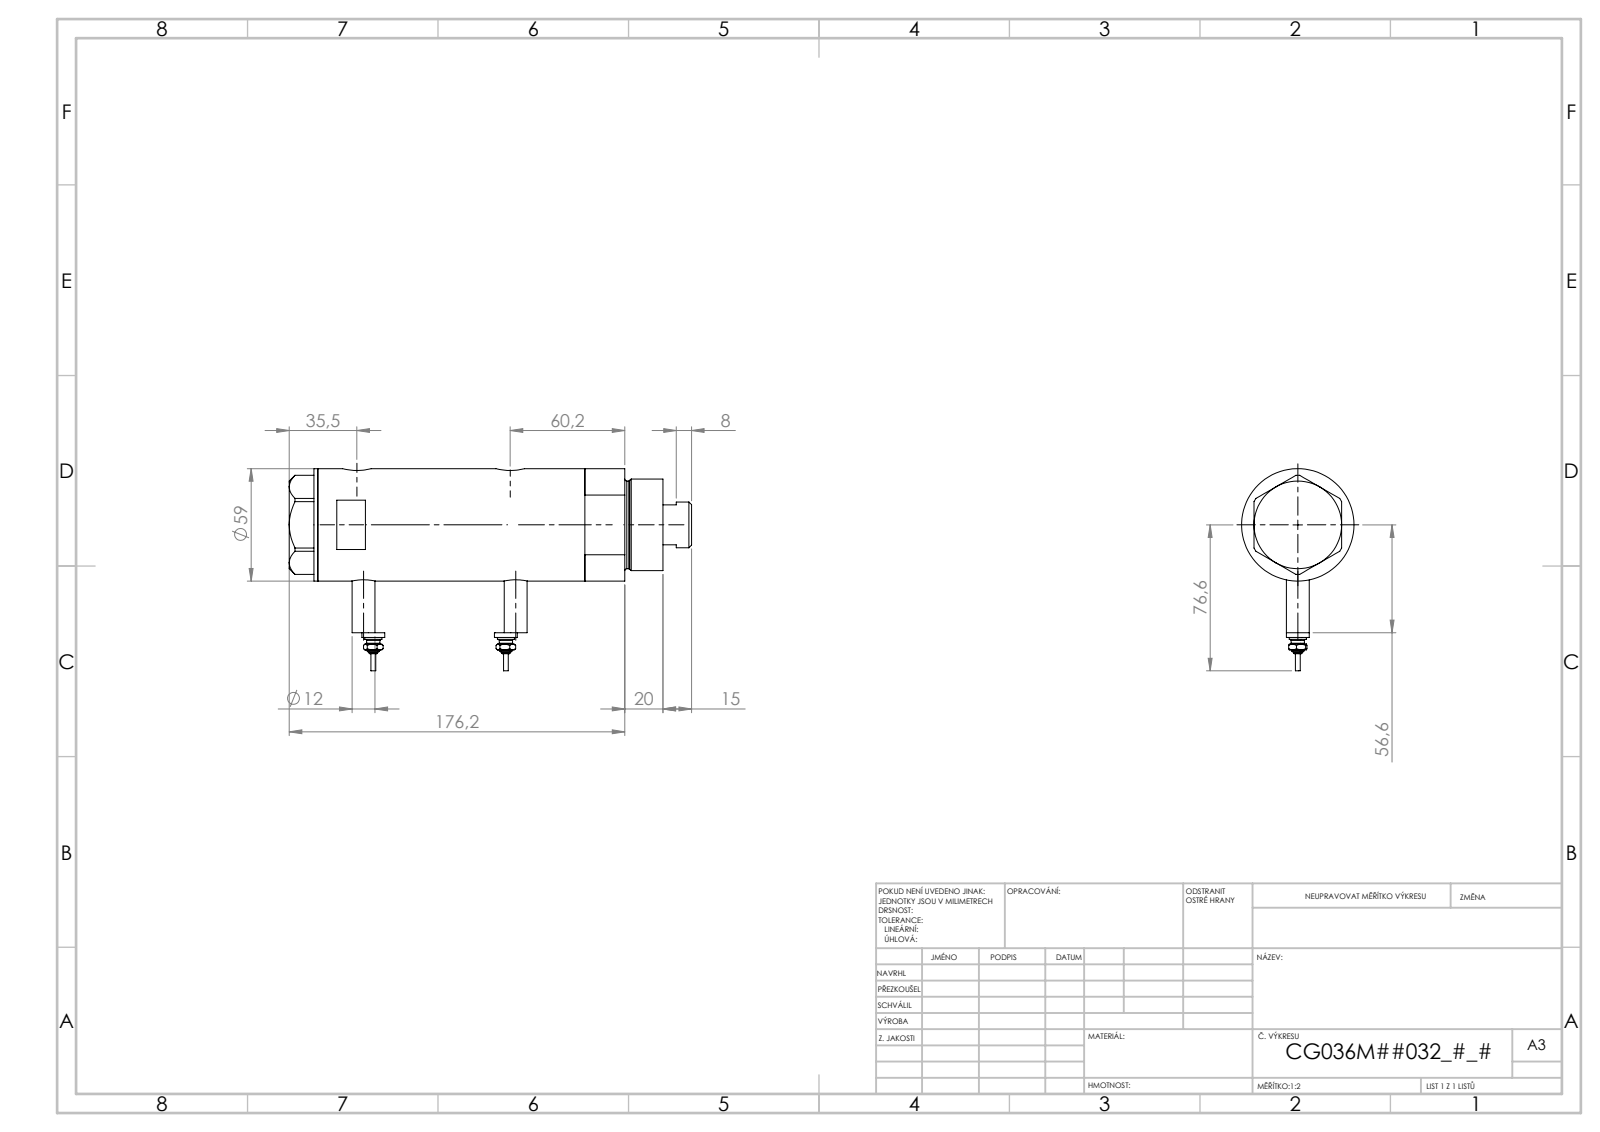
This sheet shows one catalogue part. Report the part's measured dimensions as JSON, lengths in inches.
{"part_name": "V270CG_SWITCH; V270CG_FRONT; V270CG_BACK; V270CG_VC (+1 more)", "step_written_by": "SolidWorks 2019 (CONFIG_CONTROL_DESIGN)", "units": "inches", "bodies": {"solids": 6, "faces": 232, "planar": 81, "cylindrical": 77, "other": 74}, "overall_size": [7.694, 3.594, 2.323], "volume_in3": 27.13, "surface_area_in2": 148.6, "round_holes": [[0.197, 2], [0.383, 2], [0.492, 2], [0.591, 2], [0.335, 1], [0.984, 1], [1.043, 1], [1.417, 1], [1.575, 1], [2.047, 1]], "round_bosses_or_shafts": [[0.472, 3], [0.354, 2], [0.276, 2], [0.171, 2], [0.094, 2], [2.323, 1], [1.89, 1], [1.811, 1]], "face_to_face_distances": [3.517, 0.925, 2.592, 0.591, 1.516, 4.108, 7.103, 6.513, 5.587, 2.995], "hole_center_spacings": [0.114, 0.138, 2.526, 2.64, 2.663, 2.778, 0.114, 0.115]}
